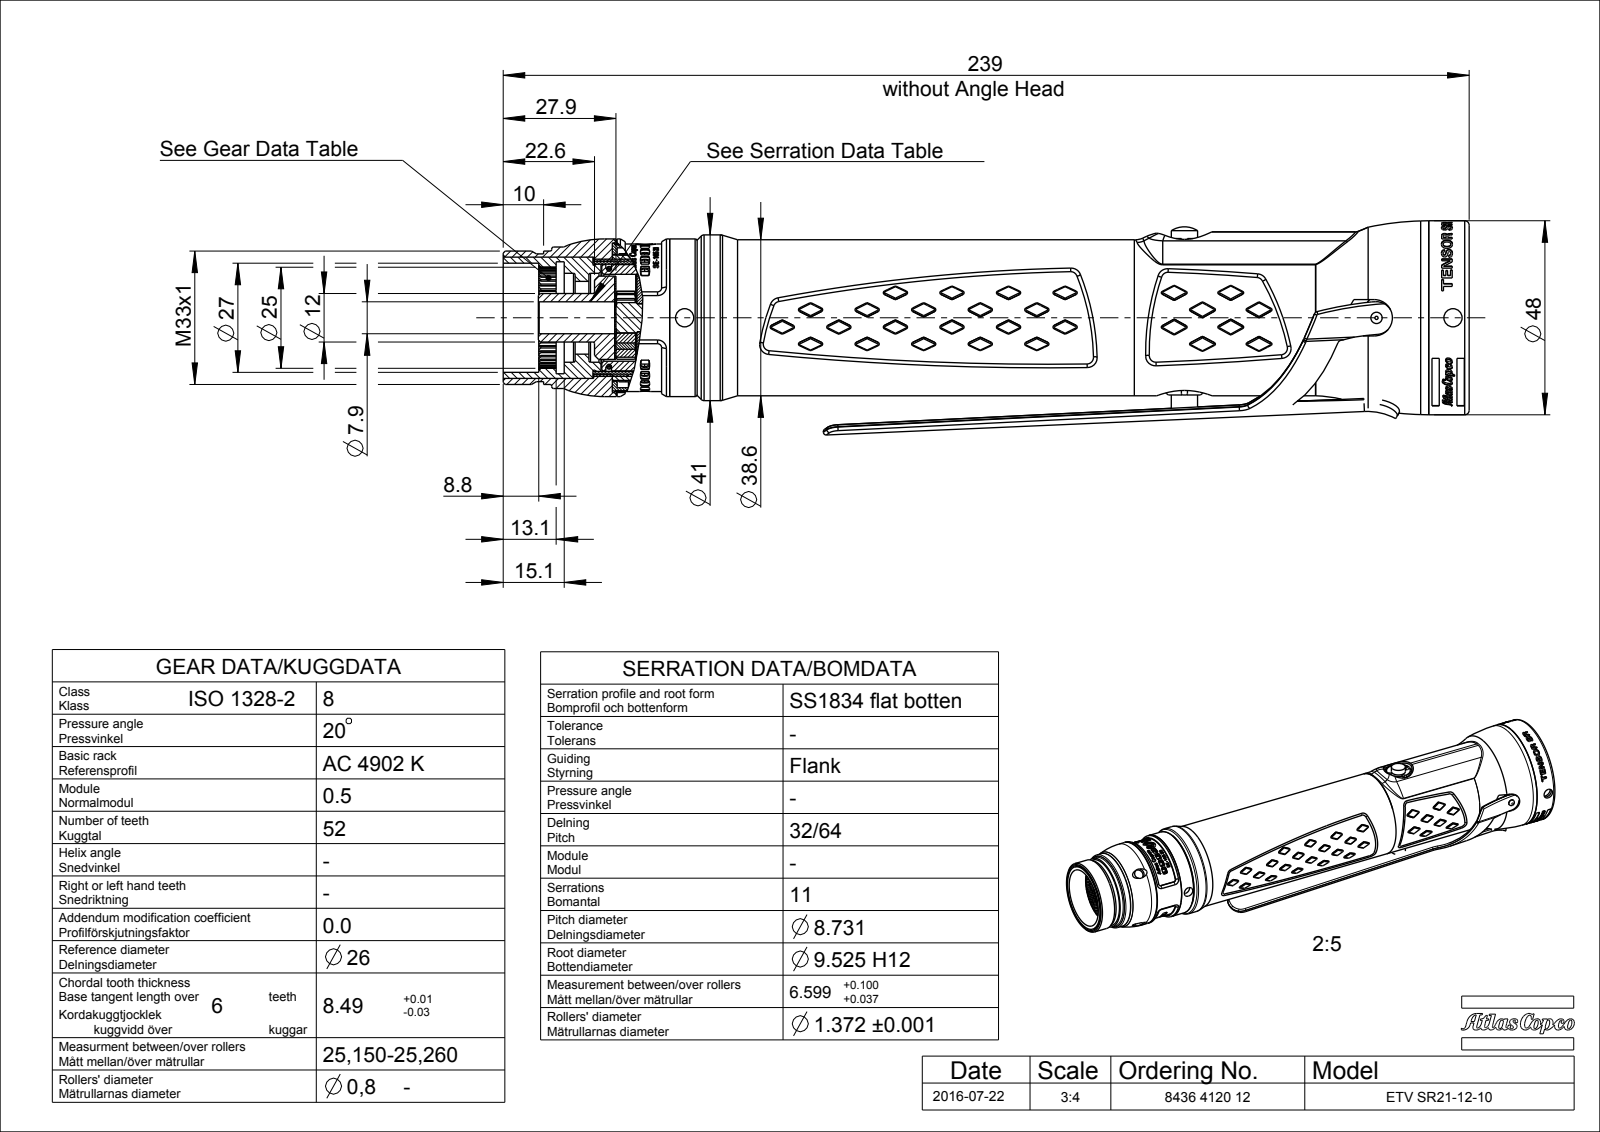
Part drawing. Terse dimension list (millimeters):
name: 4220410004; 4220011402; 4220405381_ASM; 4220406381_ASM (+8 more)
written by: PRO/ENGINEER BY PARAMETRIC TECHNOLOGY CORPORATION, 2011410 (CONFIG_CONTROL_DESIGN)
unit: mm
bodies: 50 solids, 4693 faces (1534 planar, 927 cylindrical, 2232 other)
size: 297.97 × 54.8 × 48
volume: 108 436 mm³; area: 129 801 mm²
holes: 12× ⌀3.27, 11× ⌀2.64, 11× ⌀3.6, 8× ⌀1, 7× ⌀4.5, 4× ⌀2.6, 4× ⌀2.8, 3× ⌀1.5, 2× ⌀2.5, 2× ⌀3, 2× ⌀6.5, 2× ⌀7
bosses: 4× ⌀4, 4× ⌀2.54, 4× ⌀1.9, 3× ⌀4.6, 3× ⌀3.05, 3× ⌀2.55, 3× ⌀2.3, 3× ⌀2.2
rounds: 88× R0.5, 32× R0.4, 16× R1, 8× R0.2, 8× R0.45, 8× R0.75, 4× R2, 4× R3
face distances: 2.5, 0.5, 1.2, 21, 189, 168, 1.5, 23.07, 186.5, 165.5
hole spacings: 1.5, 2.6, 4.48, 9.75, 13.79, 15, 21.21, 3
